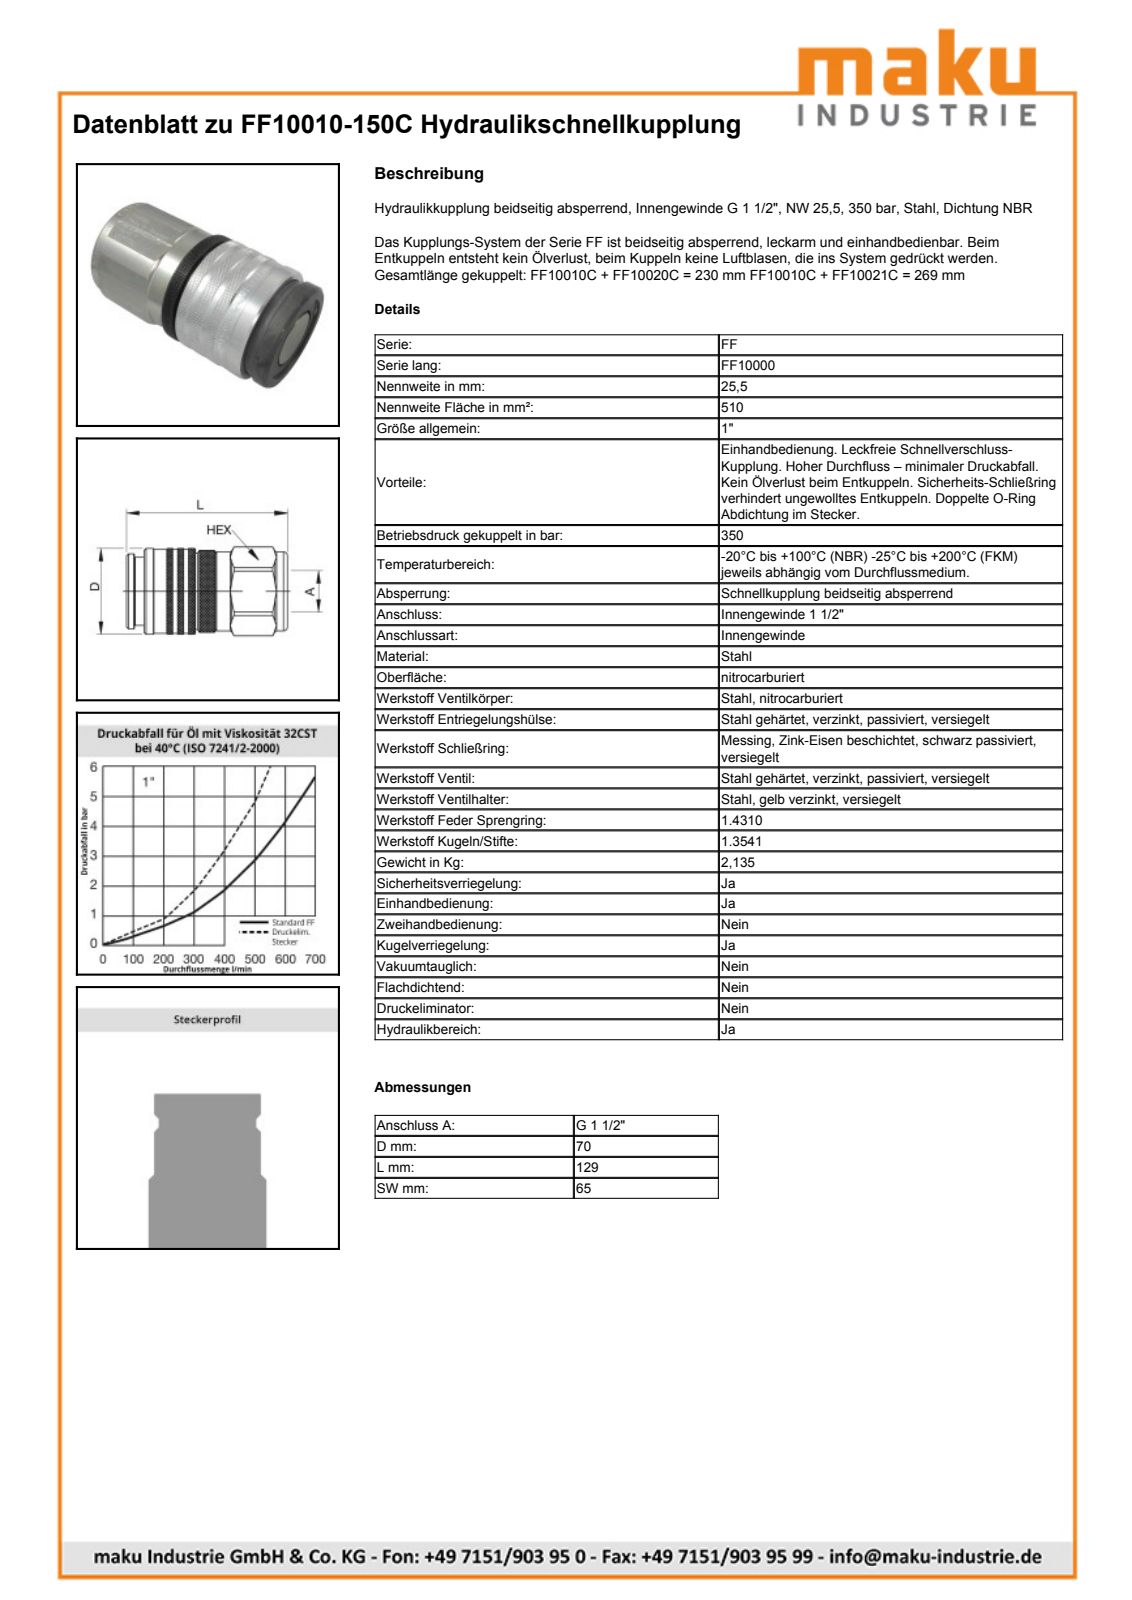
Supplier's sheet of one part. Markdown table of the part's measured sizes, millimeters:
| quantity | value |
| --- | --- |
| part name | FF10010-150C |
| STEP written by | SolidWorks 2009 (AUTOMOTIVE_DESIGN) |
| units | millimeters |
| bodies | 1 solid, 705 faces (330 planar, 131 cylindrical, 244 other) |
| overall size | 128.8 × 70 × 70 |
| volume | 414 146 mm³ |
| surface area | 41 967 mm² |
| round holes (diameter × count) | 33 × 1, 35.5 × 1, 44.85 × 1, 50 × 1, 60.3 × 1 |
| round bosses / shafts (diameter × count) | 70 × 1, 69.5 × 1, 68.5 × 1, 67.35 × 1, 65 × 1, 60 × 1, 49.8 × 1, 35 × 1 |
| partial cylindrical surfaces (radius × count) | 32.4 × 1 |
| main face-to-face distances | 65, 26.96, 127.25, 100.29, 127.3, 100.34, 128.8, 101.84, 1.55, 1.5 |
